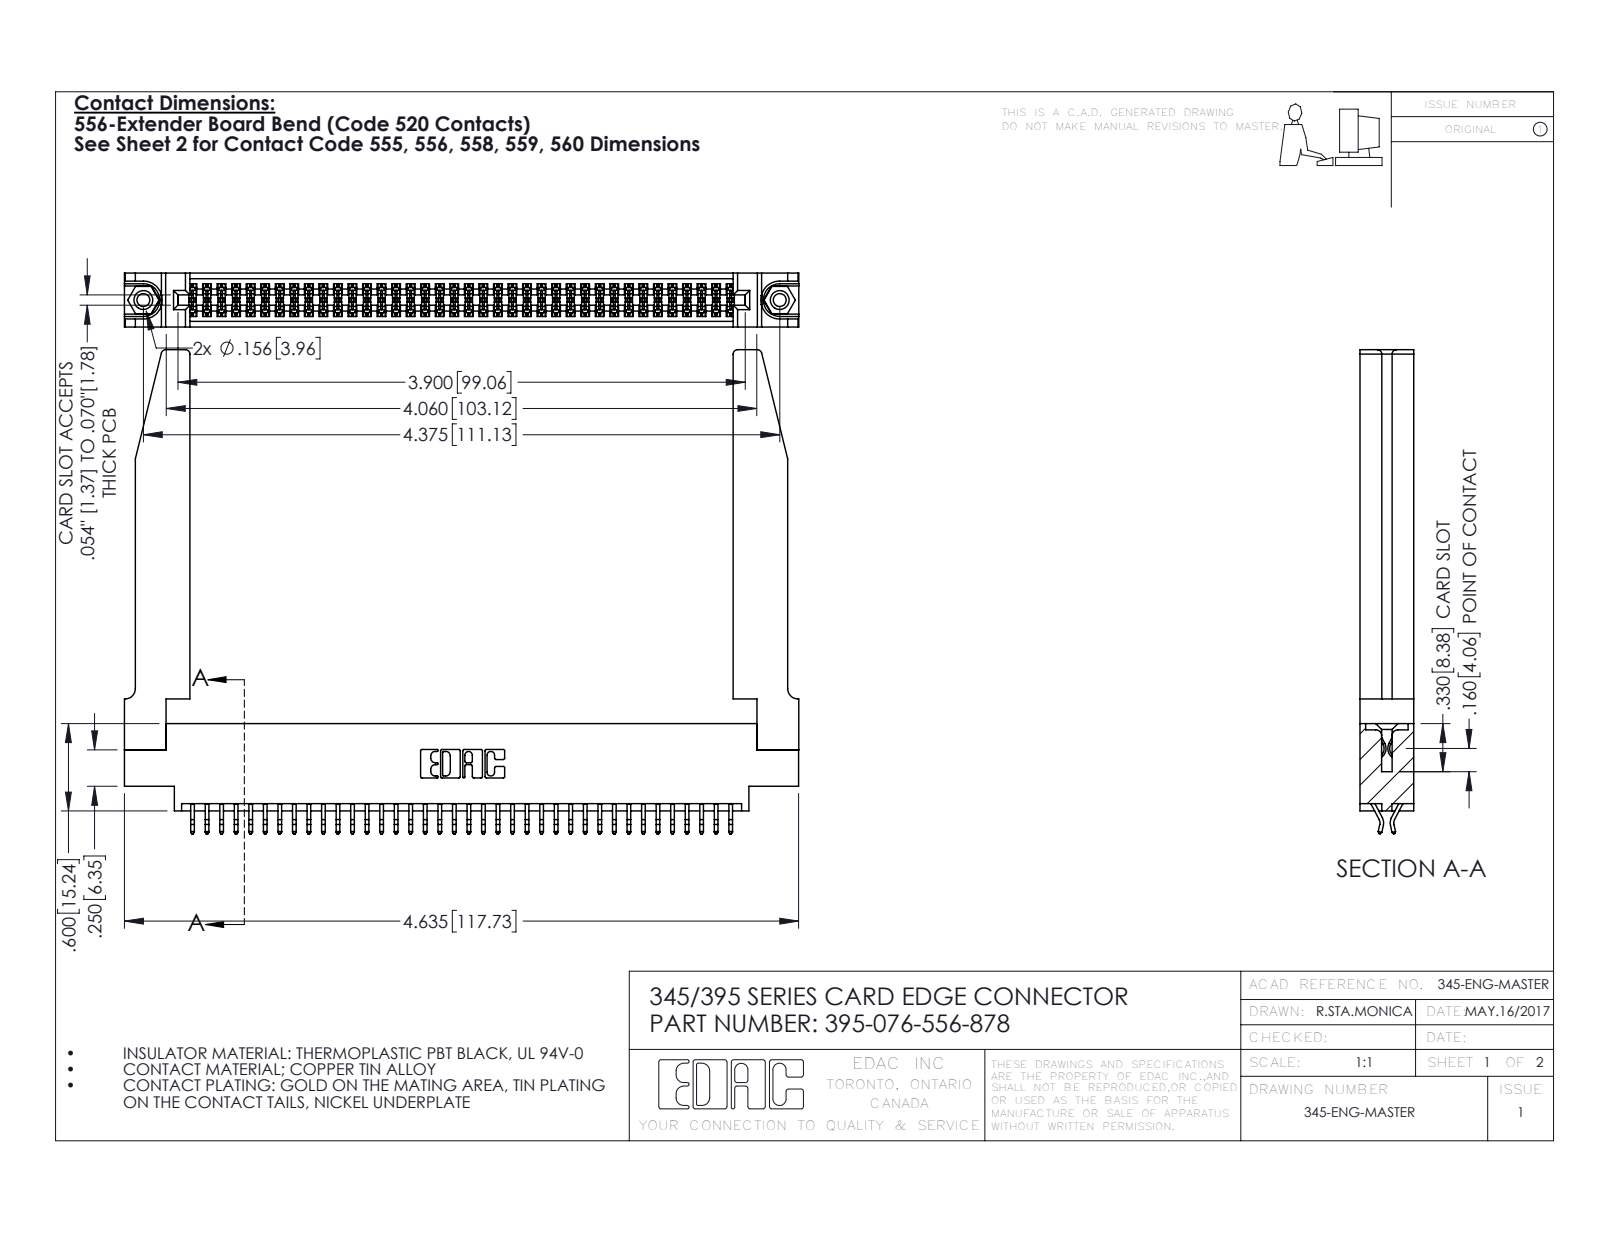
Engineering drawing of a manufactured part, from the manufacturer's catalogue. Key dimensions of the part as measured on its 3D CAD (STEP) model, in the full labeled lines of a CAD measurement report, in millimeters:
Part name (STEP PRODUCT): 345-292-001_556 Tail; 345 Part_0.170 Offset - 0.156 Dia-TH; 345-250-001_345-250-001-102; 345-220-078_345-220-078 (+1 more)
STEP written by: SolidWorks 2016 (CONFIG_CONTROL_DESIGN)
Units: millimetres
Bodies: 81 solids, 4620 faces (3038 planar, 1530 cylindrical, 52 other)
Overall size (bounding box): 117.8 × 84.5 × 9.4
Volume: 19 060 mm³ · Surface area: 23 520 mm²
Round holes (diameter × count): ⌀2.3 ×2, ⌀3.2 ×2, ⌀4 ×2, ⌀1.6 ×1
Round bosses / shafts (diameter × count): ⌀3.9 ×2
Partial cylindrical surfaces — rounded edges, fillets, slot ends (radius × count): R0.2 ×114, R0.3 ×22, R0.8 ×8, R0.2 ×6, R0.8 ×6, R0.7 ×3, R0.3 ×2, R0.4 ×2
Main face-to-face distances: 9.4, 1.8, 7.6, 0.6, 2.5, 6.9, 5.1, 5.7, 4.4, 3.8
Hole centre spacings: 6.9, 105.1, 111.1
